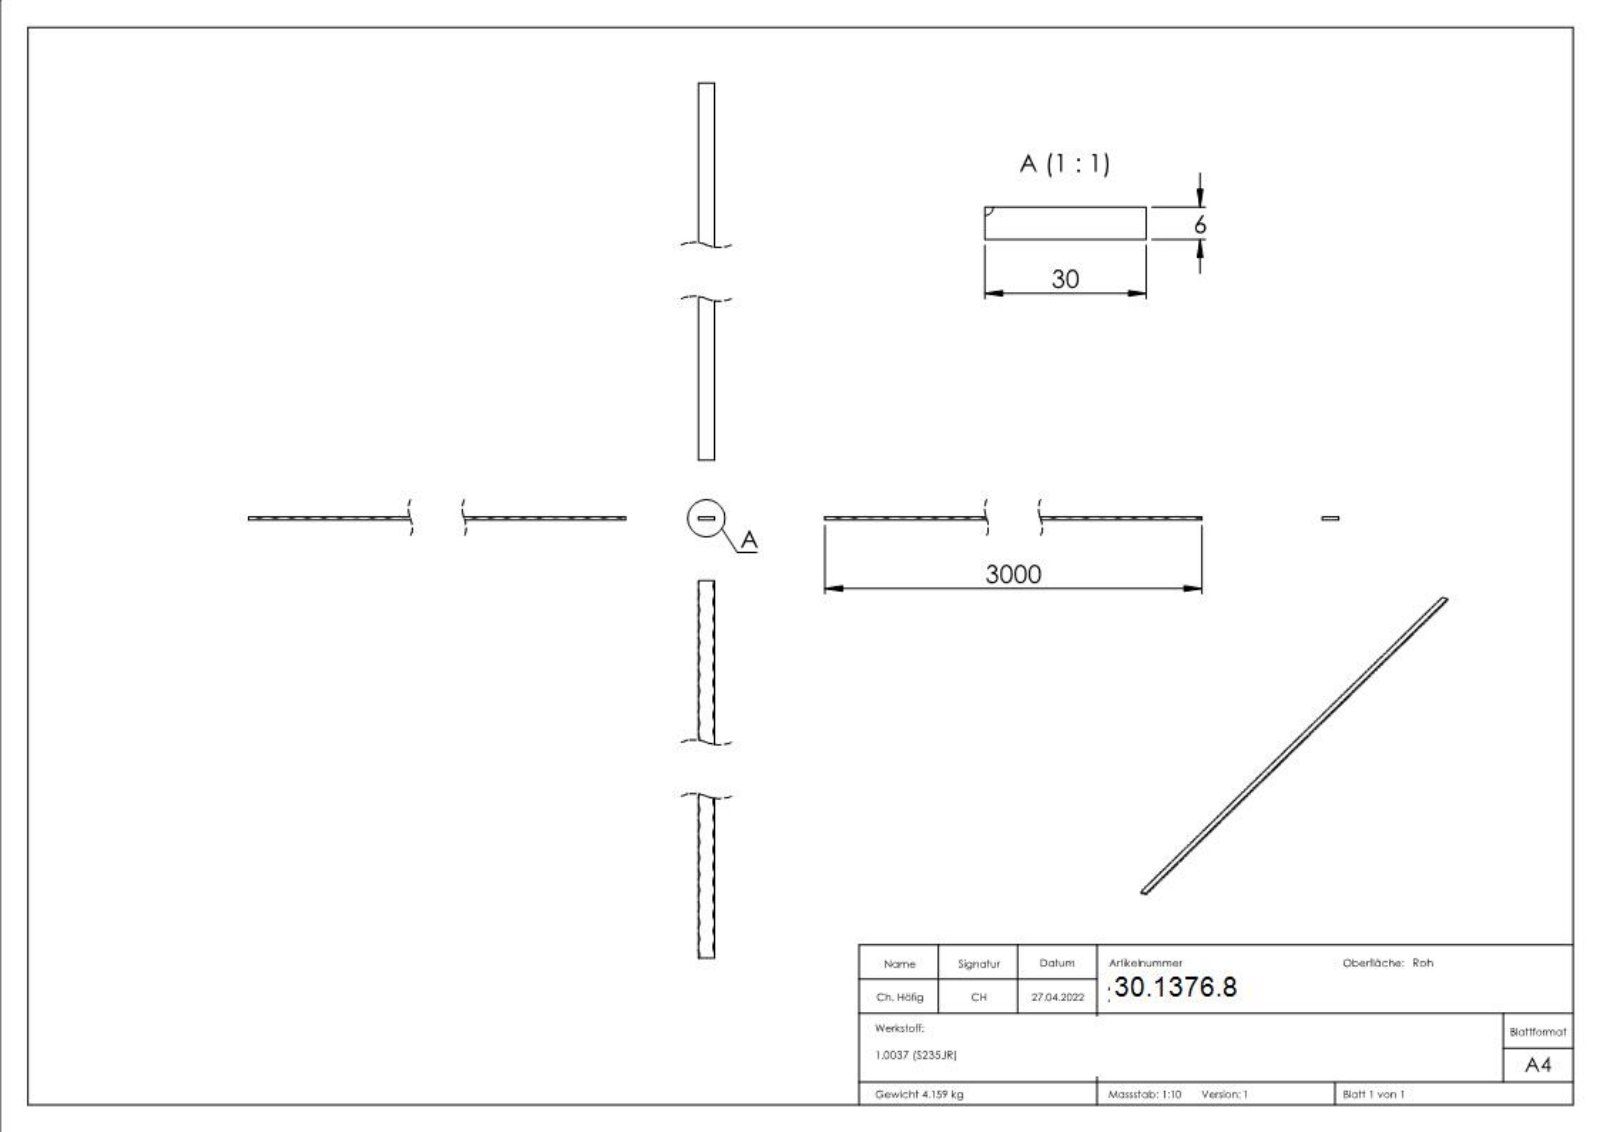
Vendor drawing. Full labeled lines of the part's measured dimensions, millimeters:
Part name (STEP PRODUCT): 2006-30
STEP written by: SolidWorks 2018 (CONFIG_CONTROL_DESIGN)
Units: millimetres
Bodies: 1 solid, 446 faces (121 planar, 0 cylindrical, 325 other)
Overall size (bounding box): 3000 × 30 × 6
Volume: 533 221 mm³ · Surface area: 214 193 mm²
Main face-to-face distances: 6, 30, 3000, 5.9, 3.66, 3.27, 0.34, 1500, 13.99, 16.01
